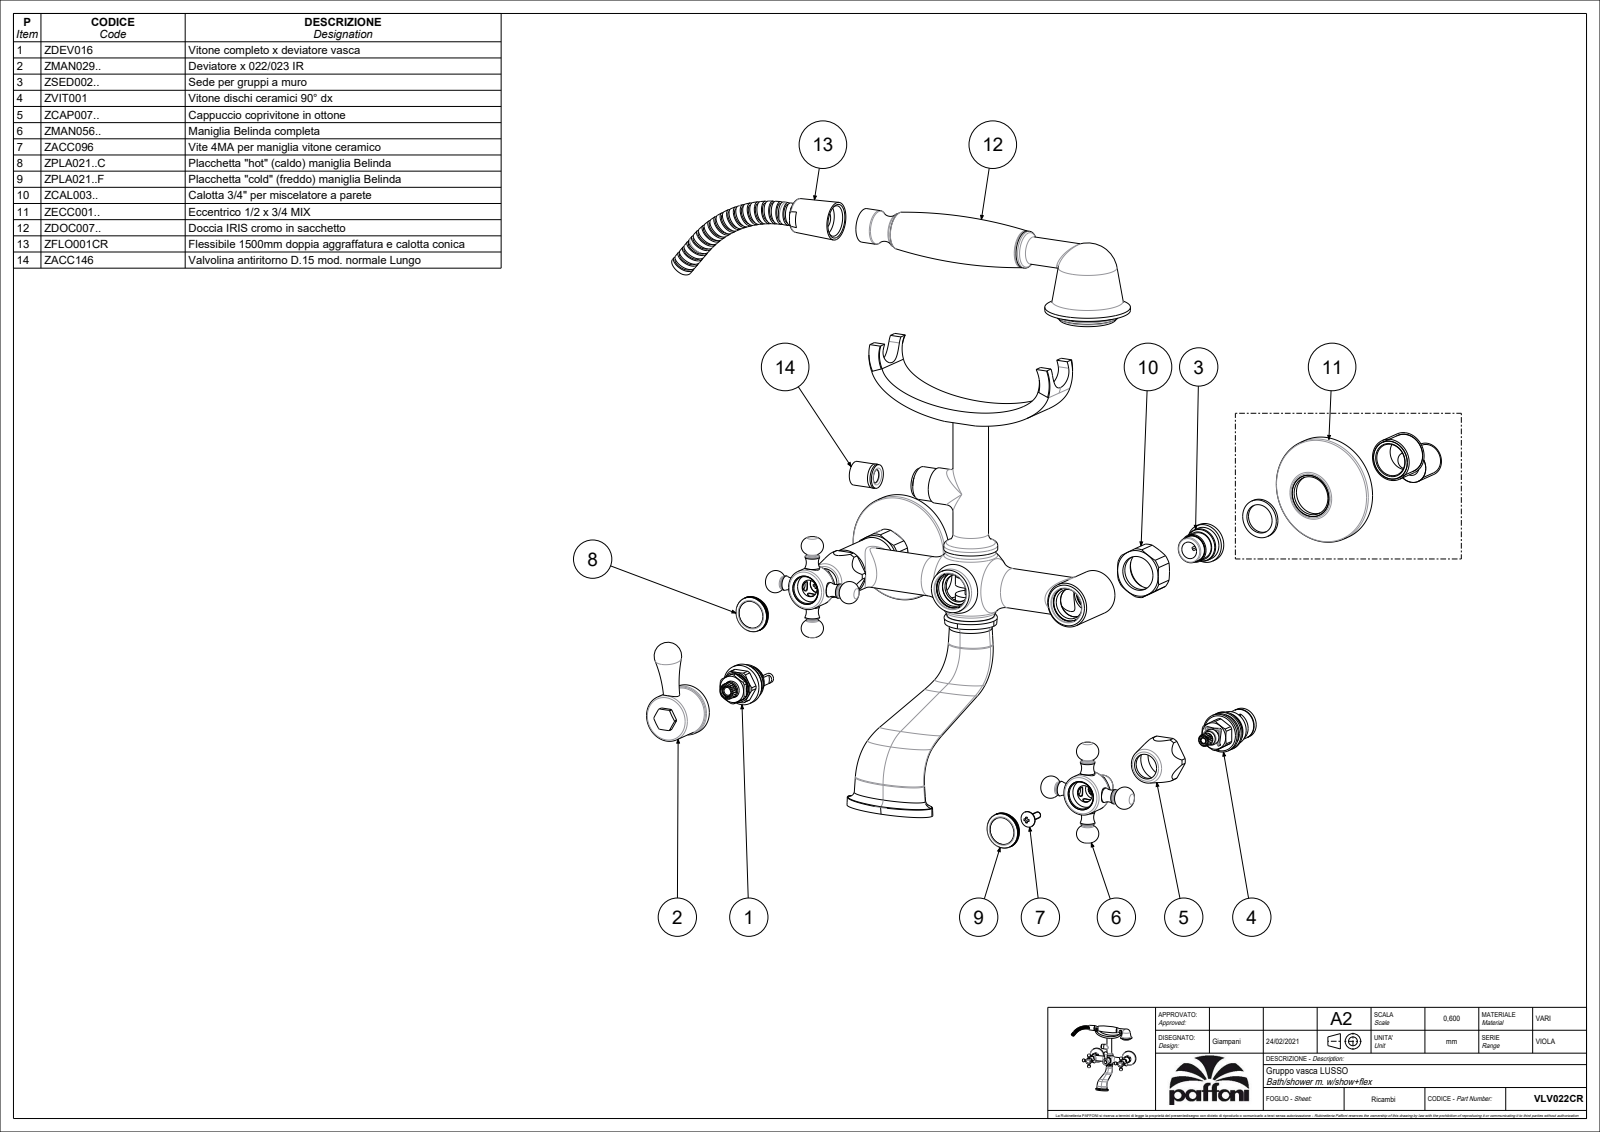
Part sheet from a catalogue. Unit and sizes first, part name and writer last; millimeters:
Units: millimetres
Overall size (bounding box): 299.05 × 280.51 × 165.32
Round holes (diameter × count): ⌀14 ×1
Round bosses / shafts (diameter × count): ⌀20.5 ×3, ⌀9 ×3, ⌀7 ×3, ⌀65.5 ×2, ⌀27.8 ×2, ⌀25 ×2, ⌀22 ×2, ⌀14 ×2
Partial cylindrical surfaces — rounded edges, fillets, slot ends (radius × count): R11 ×2, R14.5 ×2, R15.5 ×2, R7.35 ×1, R10 ×1
Main face-to-face distances: 26.5, 66.95, 40.45, 29, 227.01, 6.75, 233.01, 6, 33.7, 33.25
Volume: 640 119 mm³ · Surface area: 134 501 mm²
Bodies: 3 solids, 1262 faces (514 planar, 350 cylindrical, 398 other)
Part name (STEP PRODUCT): VLV022CR
STEP written by: CREO PARAMETRIC BY PTC INC, 2020044 (CONFIG_CONTROL_DESIGN)
